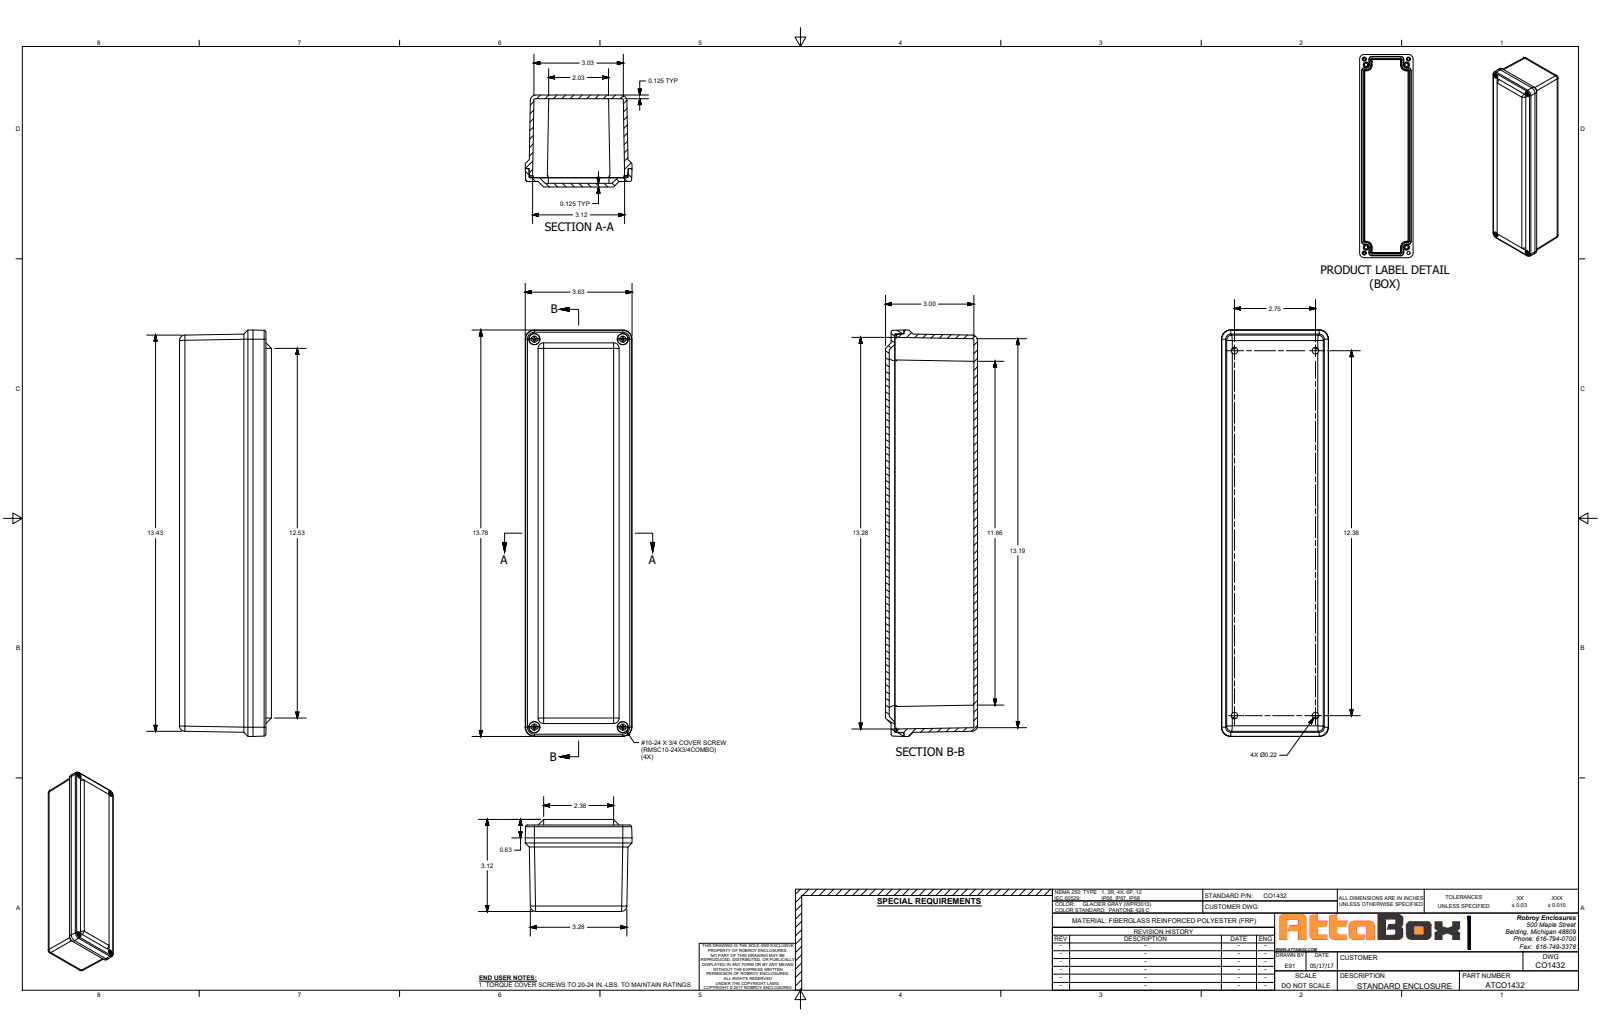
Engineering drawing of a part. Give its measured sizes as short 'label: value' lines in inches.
name: CO1432
written by: SolidWorks 2018 (AUTOMOTIVE_DESIGN)
unit: in
bodies: 11 solids, 375 faces (167 planar, 112 cylindrical, 96 other)
size: 13.783 × 3.625 × 3.12
volume: 27.62 in³; area: 422.5 in²
holes: 8× ⌀0.219, 4× ⌀0.159, 4× ⌀0.19, 4× ⌀0.375
bosses: 4× ⌀0.371, 4× ⌀0.27, 4× ⌀0.177
rounds: 20× R0.031, 16× R0.012, 8× R0.048, 4× R0.062, 4× R0.176, 4× R0.188, 4× R0.22, 4× R0.313
face distances: 0.125, 2.995, 0.122, 3.12, 2.87, 2.807, 0.187, 0.313, 0.125, 0.062
hole spacings: 0.41, 2.901, 12.766, 13.085, 2.75, 3, 12.375, 12.677
